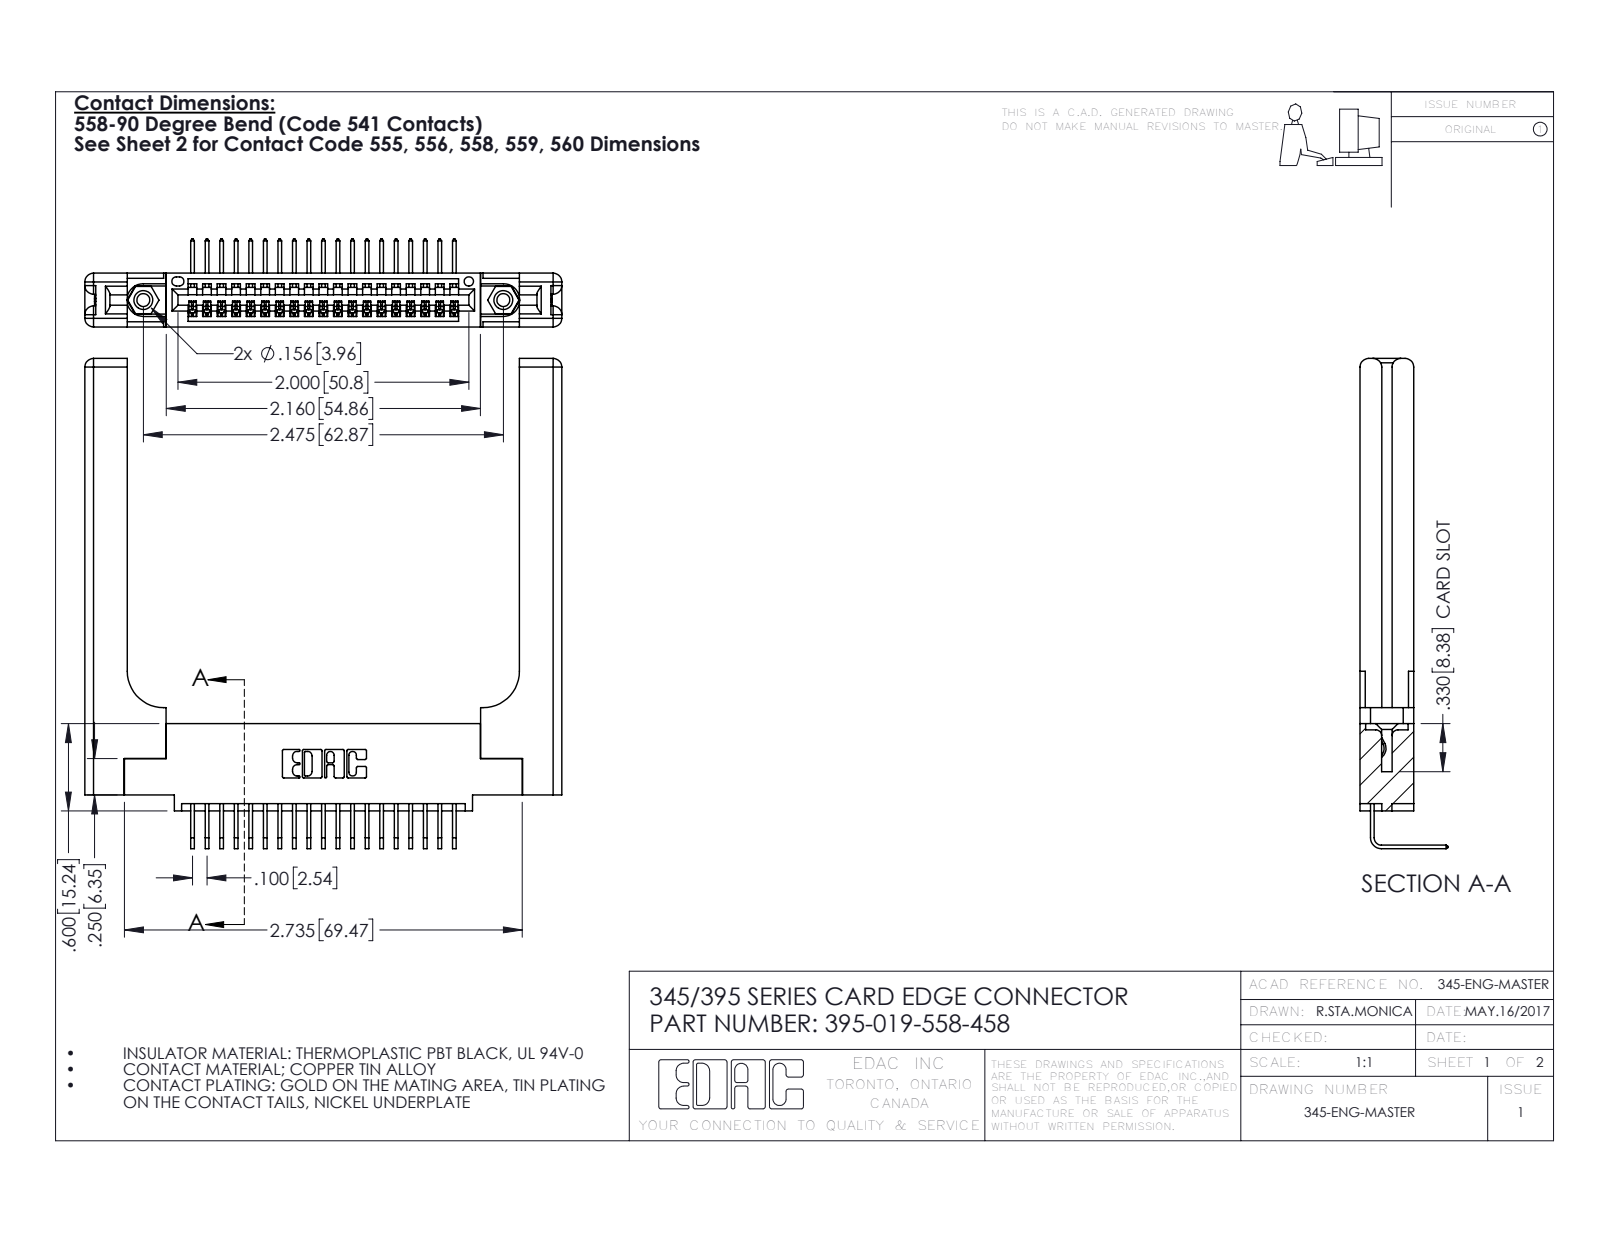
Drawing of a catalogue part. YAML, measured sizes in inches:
part_name: "345-220-058_345-220-058; 345 Part_0.110 Offset - 0.156 Dia-TH; 345-292-001_558 Tail - 2; 345-250-001_345-250-001-102 (+1 more)"
step_written_by: "SolidWorks 2016 (CONFIG_CONTROL_DESIGN)"
units: inches
bodies: {solids: 24, faces: 1526, planar: 1030, cylindrical: 436, other: 60}
overall_size: [3.369, 3.279, 0.605]
volume: 0.99
surface_area: 24.33
round_holes:
  - {diameter: 0.089, count: 2}
  - {diameter: 0.125, count: 2}
  - {diameter: 0.156, count: 2}
  - {diameter: 0.064, count: 1}
round_bosses_or_shafts:
  - {diameter: 0.155, count: 2}
partial_cylinders:
  - {radius: 0.006, count: 38}
  - {radius: 0.01, count: 22}
  - {radius: 0.06, count: 16}
  - {radius: 0.007, count: 6}
  - {radius: 0.031, count: 6}
  - {radius: 0.026, count: 3}
  - {radius: 0.03, count: 2}
  - {radius: 0.031, count: 2}
face_to_face_distances: [0.37, 0.072, 0.298, 0.15, 0.148, 0.077, 0.22, 0.2, 0.098, 0.272]
hole_center_spacings: [0.27, 2.241, 2.475]
